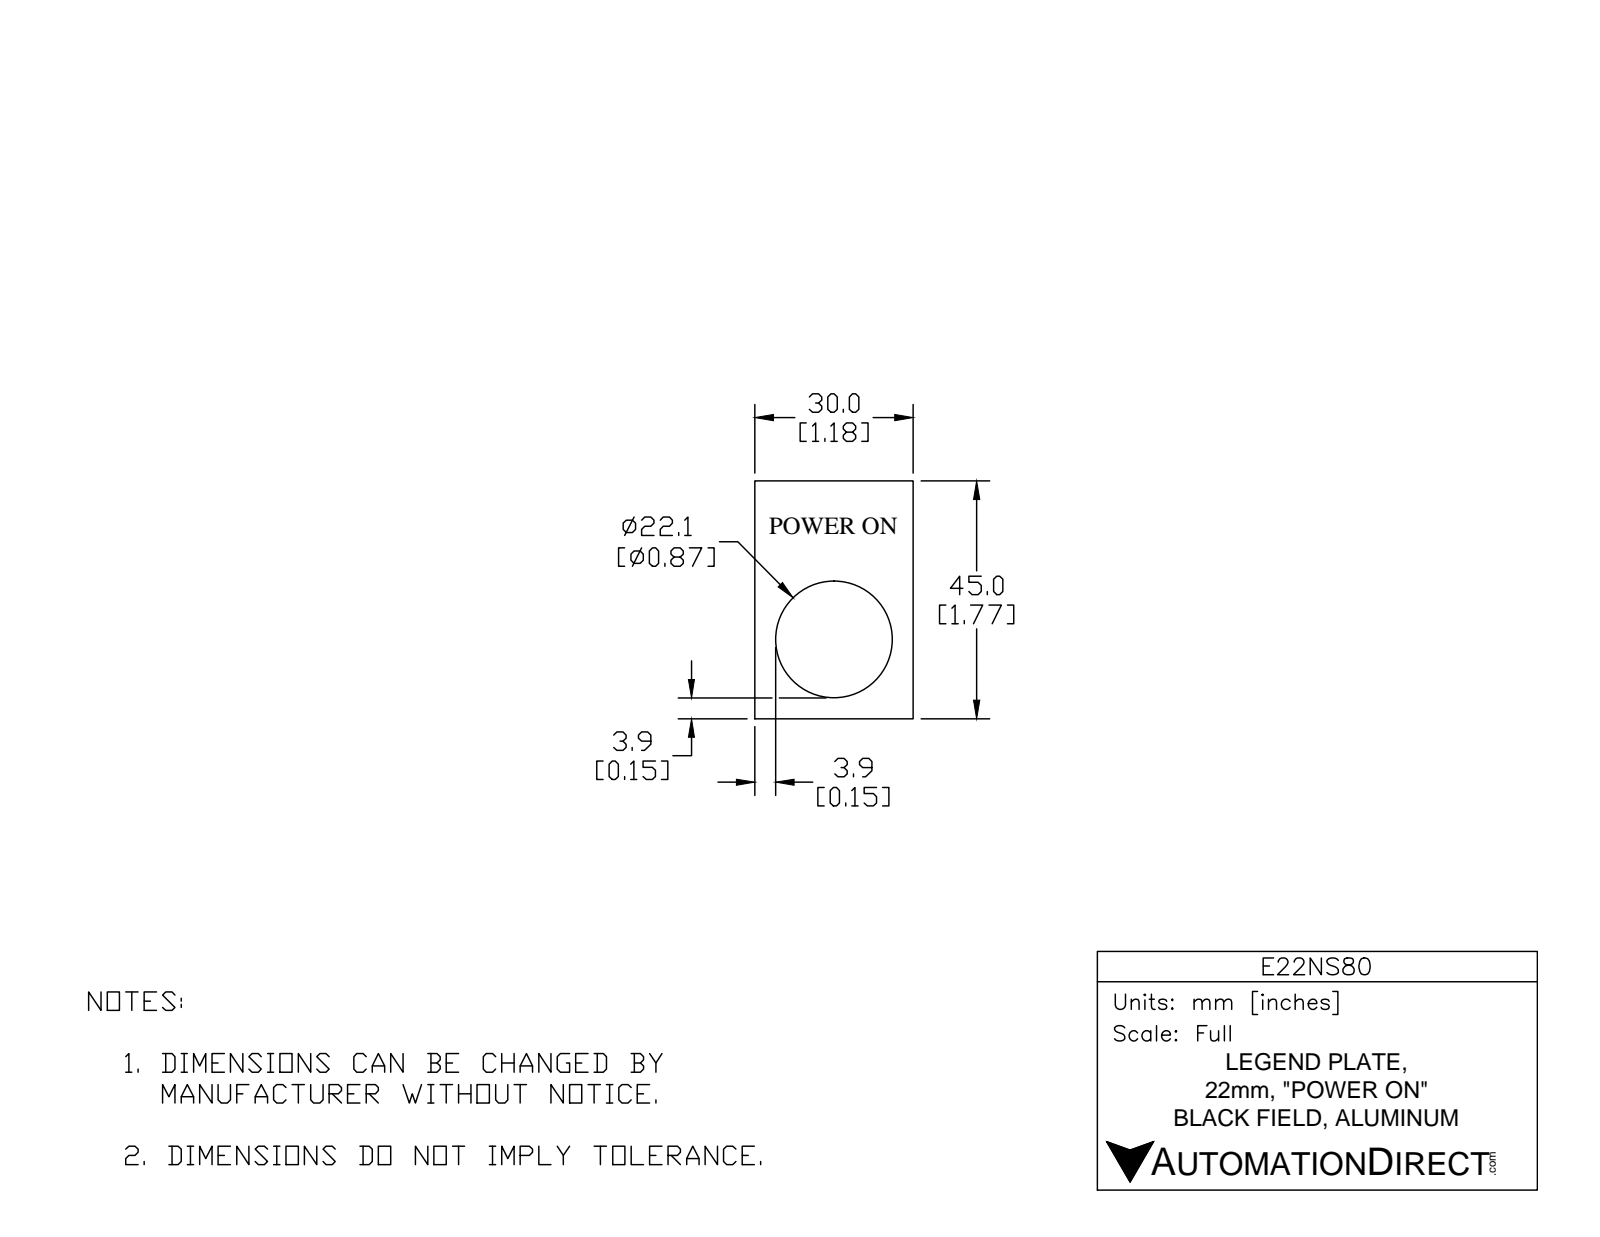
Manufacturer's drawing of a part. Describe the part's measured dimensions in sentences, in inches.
The part is named "E22NS80". Its 3-D file was written by "SolidWorks 2017 (AUTOMOTIVE_DESIGN)". It is 1 solid with 104 faces: 74 planar, 3 cylindrical and 27 other. Overall it measures 1.772 by 1.181 by 0.051 inches. Its volume is 0.076 cubic inches and its surface area 3.488 square inches. Round holes: 1 of diameter 0.874. The main face-to-face distances are 0.051, 1.181, 1.772, 0.041, 0.185, 1.587, 0.528, 0.654, 0.137, 1.044.
